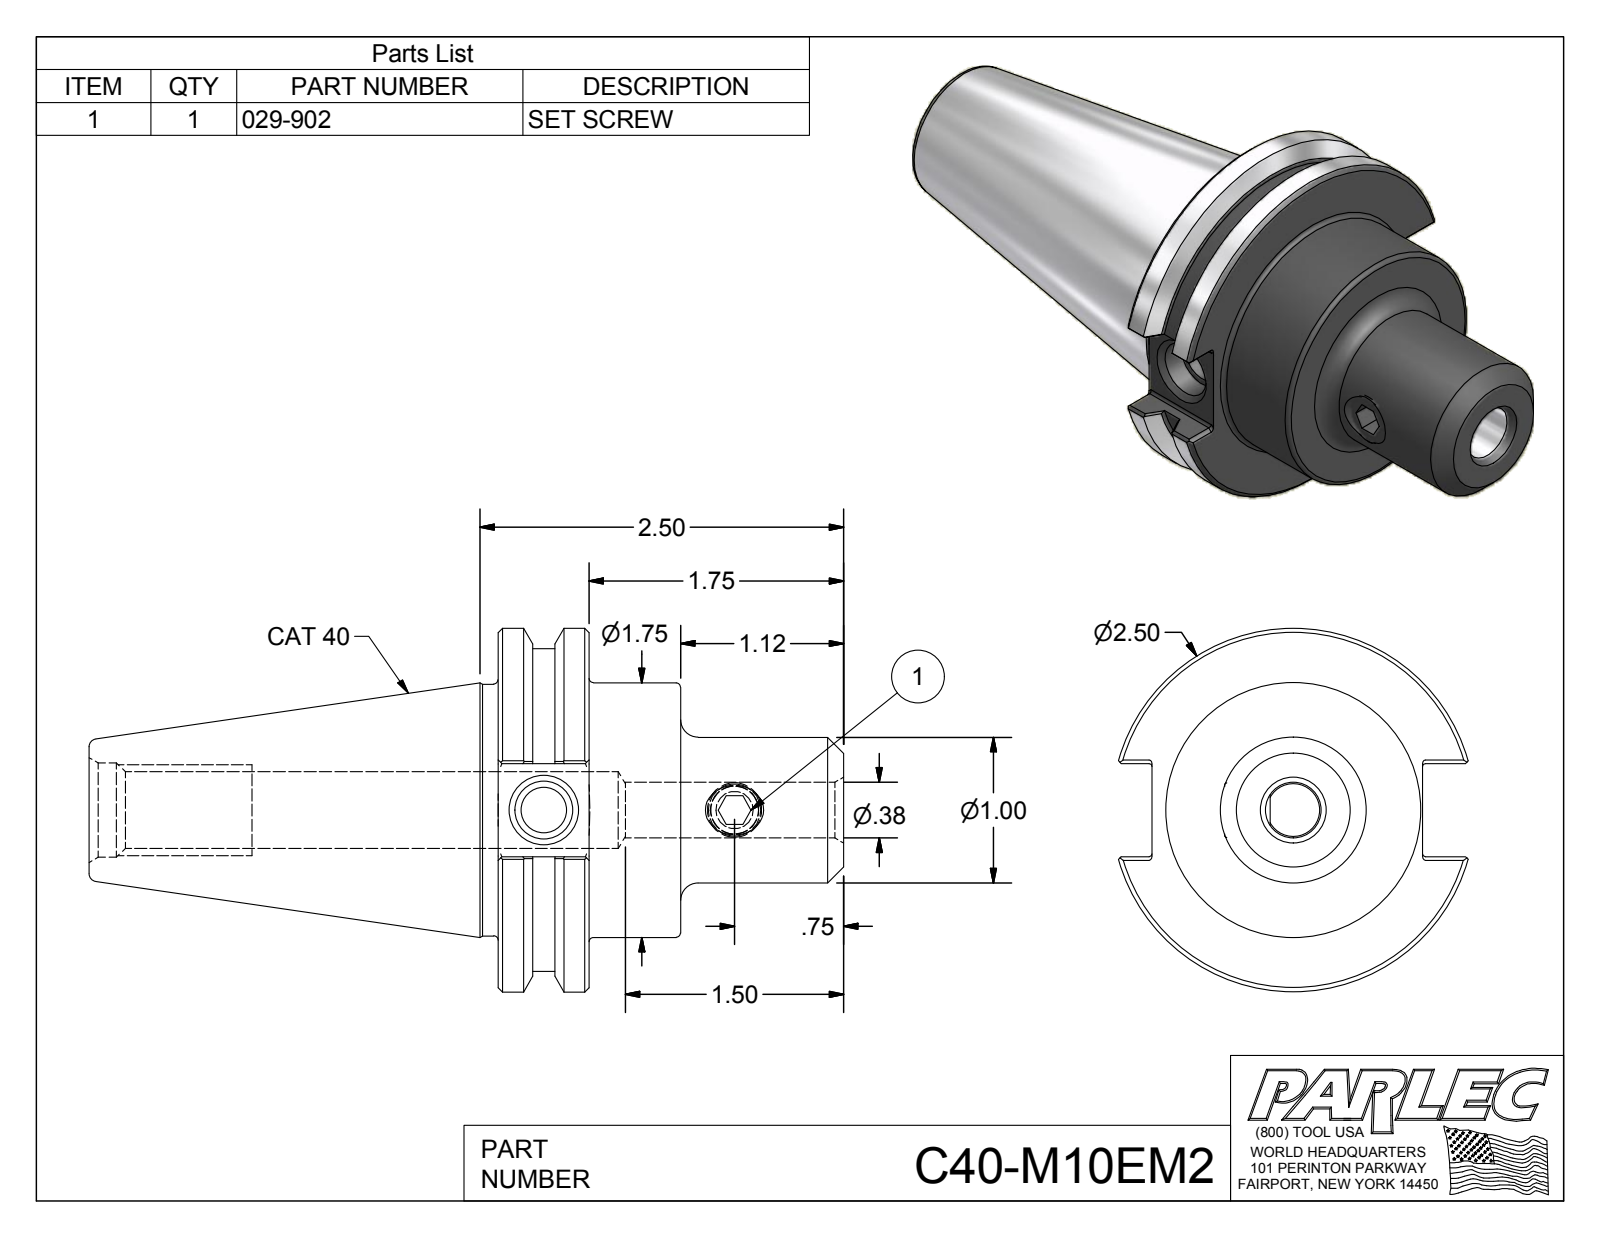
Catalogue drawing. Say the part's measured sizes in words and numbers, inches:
The part is named "C40-M10EM2; 029-902". Its 3-D file was written by "Autodesk Inventor 2012 (AUTOMOTIVE_DESIGN)". It is 2 solids with 103 faces: 42 planar, 28 cylindrical and 33 other. Overall it measures 5.187 by 2.5 by 2.406 inches. Its volume is 8.281 cubic inches and its surface area 40.96 square inches. Round holes: 1 of diameter 0.315, 1 of diameter 0.33, 1 of diameter 0.384, 1 of diameter 0.399, 1 of diameter 0.527, 1 of diameter 0.648. Round bosses or shafts: 1 of diameter 2.5, 1 of diameter 2.219, 1 of diameter 1.75, 1 of diameter 1.73, 1 of diameter 1, 1 of diameter 0.375. Partial cylindrical surfaces (rounded edges, fillets, slot ends): 12 of radius 0.02. The main face-to-face distances are 0.625, 1.255, 0.63, 2.375, 1.75, 1.12, 0.64, 0.236, 1.86, 2.812. The hole center spacings are 1.31.
